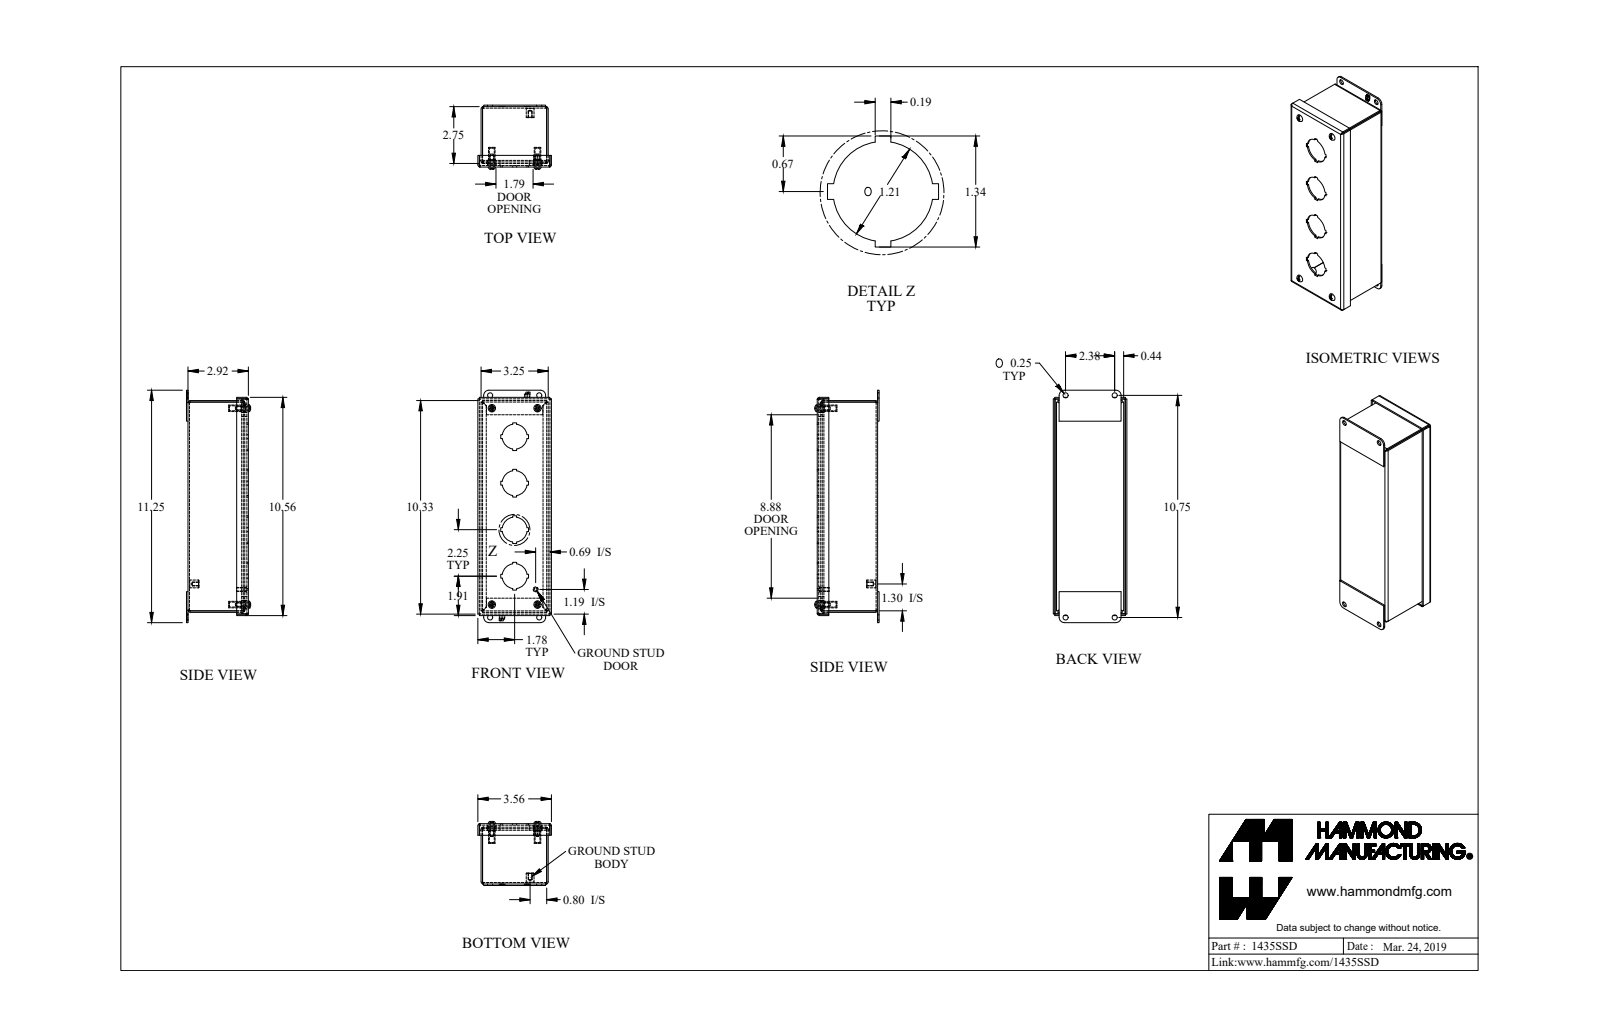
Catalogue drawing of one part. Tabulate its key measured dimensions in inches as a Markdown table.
| quantity | value |
| --- | --- |
| part name | 1435SSD_Default |
| STEP written by | SolidWorks 2019 (CONFIG_CONTROL_DESIGN) |
| units | inches |
| bodies | 19 solids, 509 faces (331 planar, 148 cylindrical, 30 other) |
| overall size | 11.25 × 3.562 × 3.104 |
| volume | 14.61 in³ |
| surface area | 381.6 in² |
| round holes (diameter × count) | 0.25 × 8, 0.065 × 4, 0.239 × 4, 0.253 × 4, 0.406 × 4, 1.21 × 4, 0.156 × 1 |
| round bosses / shafts (diameter × count) | 0.19 × 5, 0.406 × 4, 0.315 × 4, 0.148 × 4, 0.375 × 1, 0.25 × 1 |
| partial cylindrical surfaces (radius × count) | 0.036 × 12, 0.108 × 12, 0.171 × 4, 0.25 × 4 |
| main face-to-face distances | 0.072, 2.85, 0.072, 3.178, 2.922, 2.778, 3.25, 3.106, 10.178, 0.156 |
| hole center spacings | 8.2, 9.5, 10.126, 10.381, 9.754, 0.63, 0.631, 1.764 |
